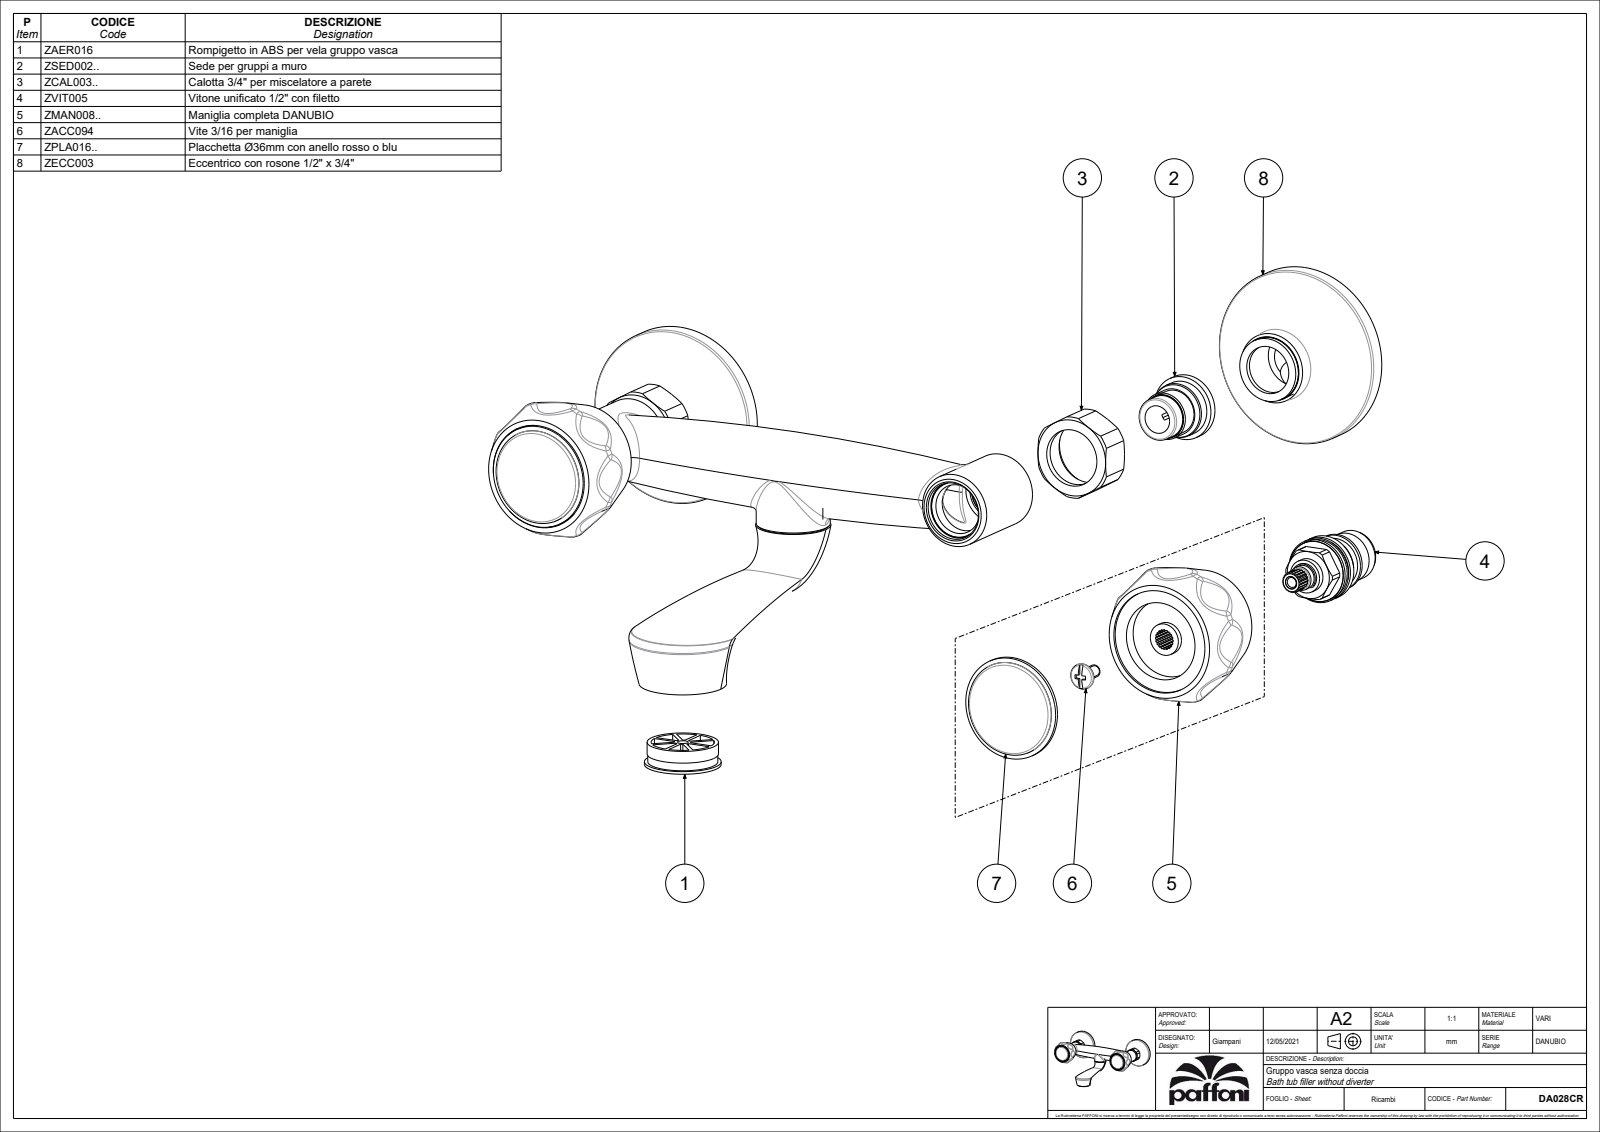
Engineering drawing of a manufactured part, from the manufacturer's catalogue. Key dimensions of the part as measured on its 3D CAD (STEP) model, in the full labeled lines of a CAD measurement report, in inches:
Part name (STEP PRODUCT): DA028CR
STEP written by: CREO PARAMETRIC BY PTC INC, 2020044 (CONFIG_CONTROL_DESIGN)
Units: inches
Bodies: 3 solids, 729 faces (226 planar, 218 cylindrical, 285 other)
Overall size (bounding box): 8.819 × 6.102 × 3.78
Volume: 10.32 in³ · Surface area: 169.7 in²
Round holes (diameter × count): ⌀0.846 ×3, ⌀0.984 ×3, ⌀0.413 ×2, ⌀0.709 ×2, ⌀0.949 ×2, ⌀1.051 ×2, ⌀1.409 ×2, ⌀1.535 ×2, ⌀2.575 ×2, ⌀0.157 ×1, ⌀0.598 ×1, ⌀0.827 ×1
Round bosses / shafts (diameter × count): ⌀1.083 ×3, ⌀2.598 ×2, ⌀1.516 ×2, ⌀1.201 ×2, ⌀1.008 ×2, ⌀0.945 ×2, ⌀0.886 ×2, ⌀0.827 ×2
Partial cylindrical surfaces — rounded edges, fillets, slot ends (radius × count): R0.039 ×28, R0.839 ×16, R0.118 ×3, R0.197 ×2, R0.394 ×2, R0.61 ×2
Main face-to-face distances: 1.142, 1.969, 0.236, 0.059, 0.374, 3.11, 0.264, 0.295, 1.732, 1.39
Hole centre spacings: 3.228, 6.22
